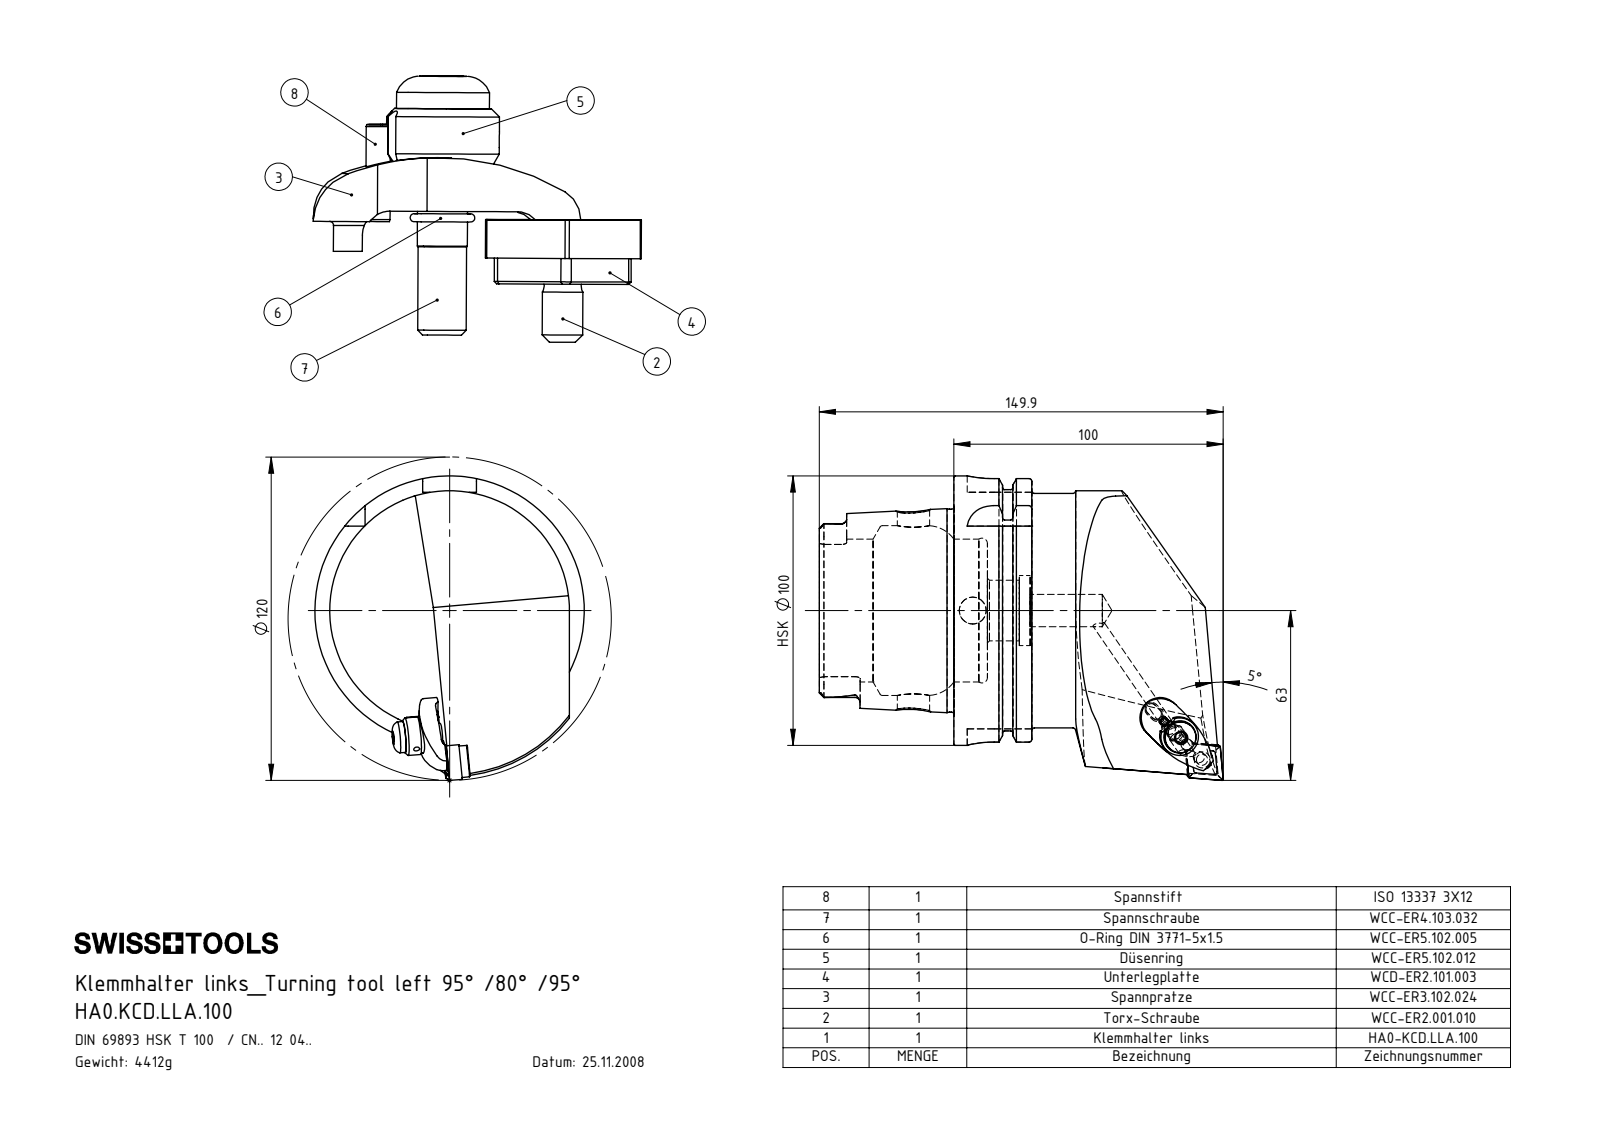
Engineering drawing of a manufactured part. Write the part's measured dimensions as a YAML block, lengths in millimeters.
part_name: "WCC-ER5.102.012_B; HA0-KCD.LLA.100_C_Fertigbearbeitung; WCD-ER2.101.003_A; HA0.KCD.LLA.100 (+7 more)"
step_written_by: "SolidWorks 2017 (AUTOMOTIVE_DESIGN)"
units: millimeters
bodies: {solids: 11, faces: 468, planar: 120, cylindrical: 154, other: 194}
overall_size: [149.9, 113, 100]
volume: 560873
surface_area: 74431
round_holes:
  - {diameter: 2, count: 3}
  - {diameter: 5, count: 3}
  - {diameter: 4.2, count: 2}
  - {diameter: 7, count: 2}
  - {diameter: 12, count: 2}
  - {diameter: 2.4, count: 1}
  - {diameter: 3, count: 1}
  - {diameter: 5.16, count: 1}
  - {diameter: 6, count: 1}
  - {diameter: 6.2, count: 1}
  - {diameter: 6.4, count: 1}
  - {diameter: 8.5, count: 1}
round_bosses_or_shafts:
  - {diameter: 6, count: 2}
  - {diameter: 3, count: 2}
  - {diameter: 100, count: 1}
  - {diameter: 91.95, count: 1}
  - {diameter: 87, count: 1}
  - {diameter: 75.26, count: 1}
  - {diameter: 14, count: 1}
  - {diameter: 11.5, count: 1}
partial_cylinders:
  - {radius: 0.39, count: 6}
  - {radius: 1.9, count: 6}
  - {radius: 0.4, count: 4}
  - {radius: 1, count: 4}
  - {radius: 10, count: 4}
  - {radius: 0.69, count: 3}
  - {radius: 0.69, count: 3}
  - {radius: 1.5, count: 3}
face_to_face_distances: [12.45, 28.95, 16.5, 49.9, 62.35, 78.85, 87.8, 78.2, 28.3, 15.85]
hole_center_spacings: [7.99, 8, 8.19, 14.67, 14.94, 14.95, 15, 22.94]
